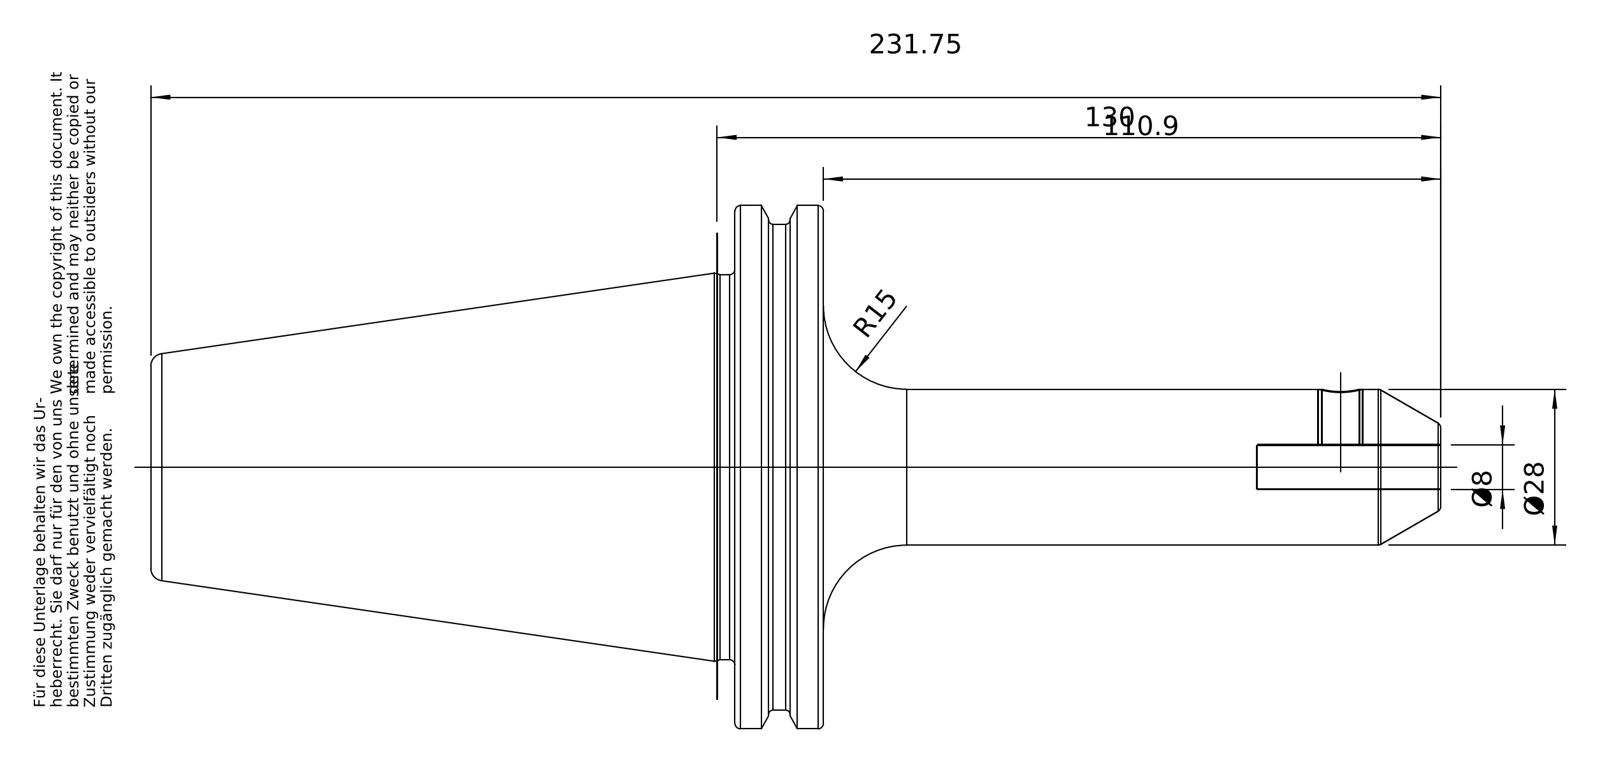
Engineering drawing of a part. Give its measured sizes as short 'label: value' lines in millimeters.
name: 50-304-08
written by: PRO/ENGINEER BY PARAMETRIC TECHNOLOGY CORPORATION, 2010430 (CONFIG_CONTROL_DESIGN)
unit: mm
bodies: 1 solid, 105 faces (23 planar, 32 cylindrical, 50 other)
size: 231.6 × 97.47 × 94
volume: 408 314 mm³; area: 52 608 mm²
holes: 2× ⌀8, 1× ⌀6.8, 1× ⌀20.75, 1× ⌀25.01, 1× ⌀25.7
bosses: 1× ⌀91, 1× ⌀69.15, 1× ⌀28, 1× ⌀24.01
rounds: 5× R1.75, 1× R48.74
face distances: 15.85, 104.8, 120.65, 72.8, 25.8, 48, 56.8, 72.65, 231.6, 183.6
